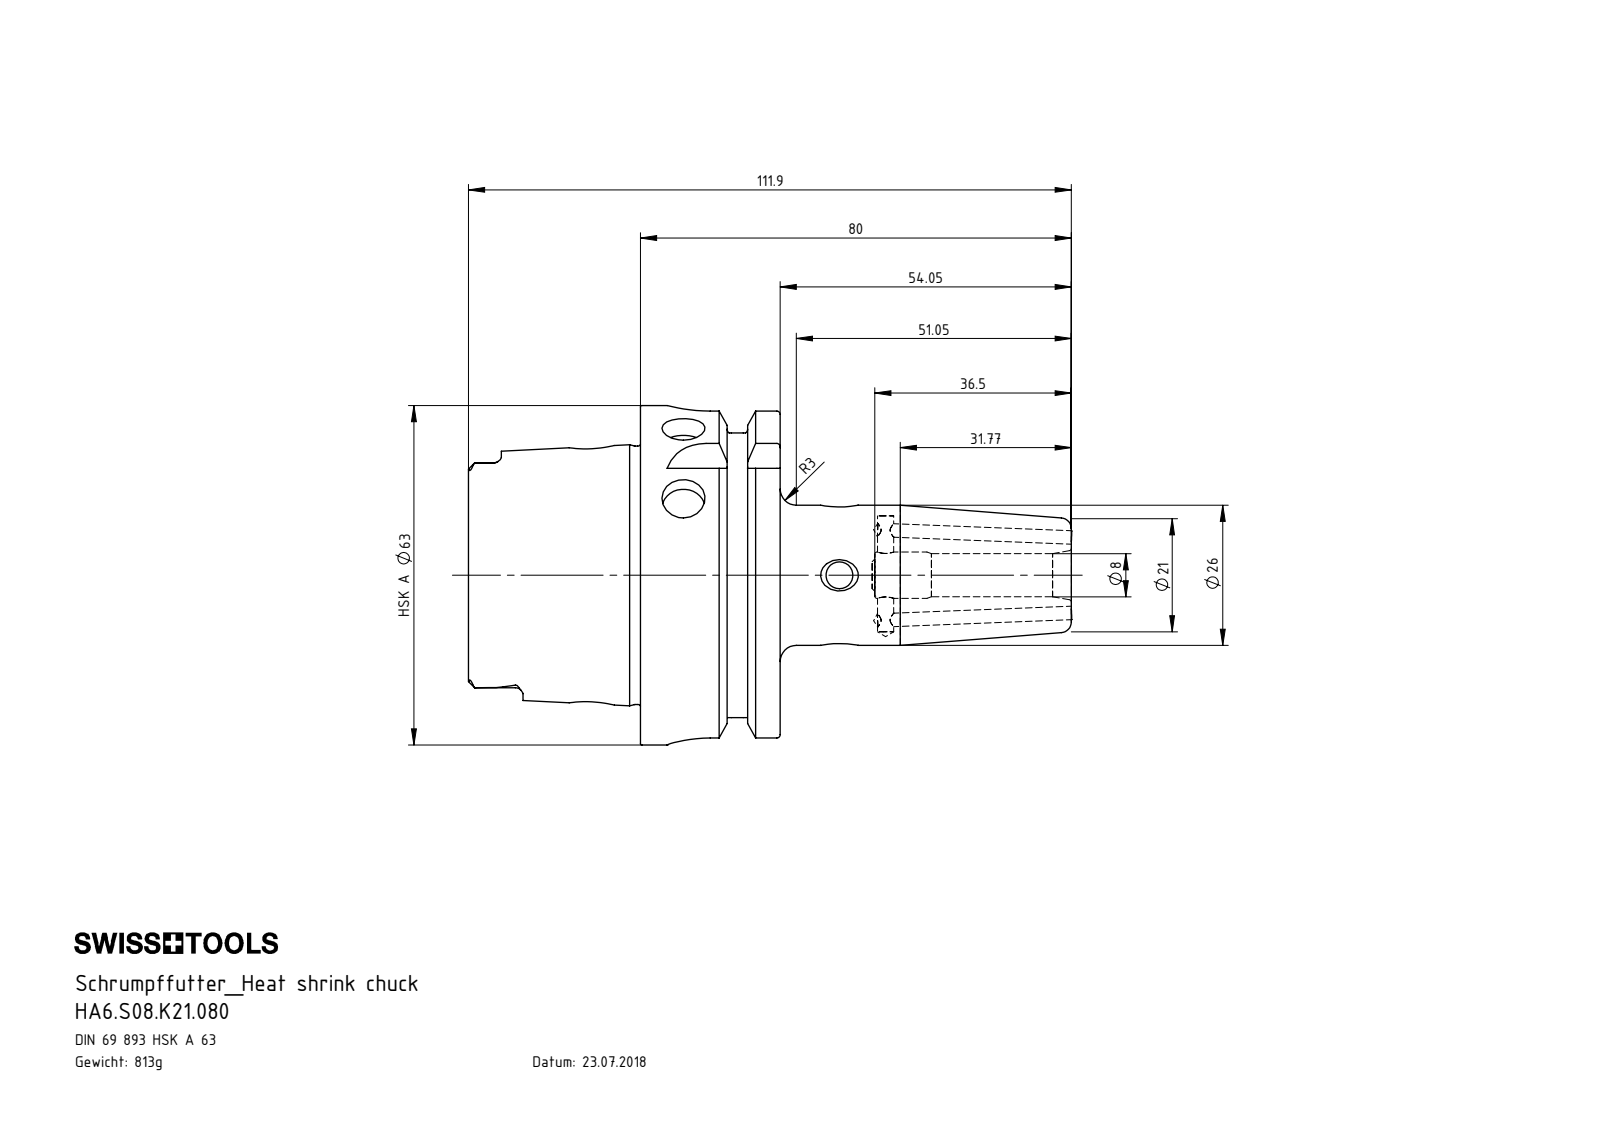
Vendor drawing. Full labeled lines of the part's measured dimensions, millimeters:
Part name (STEP PRODUCT): ERU-CJ2.001.006; ERU-AN2.K01.016_A; HA6-S08.K21.080_C_Fertigbearbeitung; HA6-S08.K21.080
STEP written by: SolidWorks 2012 (CONFIG_CONTROL_DESIGN)
Units: millimetres
Bodies: 4 solids, 309 faces (101 planar, 85 cylindrical, 123 other)
Overall size (bounding box): 111.98 × 63 × 63
Volume: 103 580 mm³ · Surface area: 29 260 mm²
Round holes (diameter × count): ⌀5 ×3, ⌀8 ×3, ⌀2.5 ×2, ⌀3 ×2, ⌀7.5 ×1, ⌀8.4 ×1, ⌀8.6 ×1, ⌀10 ×1, ⌀17 ×1, ⌀19 ×1, ⌀34 ×1, ⌀40 ×1
Round bosses / shafts (diameter × count): ⌀3 ×2, ⌀63 ×1, ⌀54.95 ×1, ⌀47.94 ×1, ⌀26 ×1, ⌀6 ×1
Partial cylindrical surfaces — rounded edges, fillets, slot ends (radius × count): R1.4 ×6, R2.88 ×4, R8 ×4
Main face-to-face distances: 25.95, 16, 9.95, 31.9, 41.85, 57.85, 52.8, 21.8, 11.85, 53.7
Hole centre spacings: 8.55, 29.95, 45.95, 54.5
